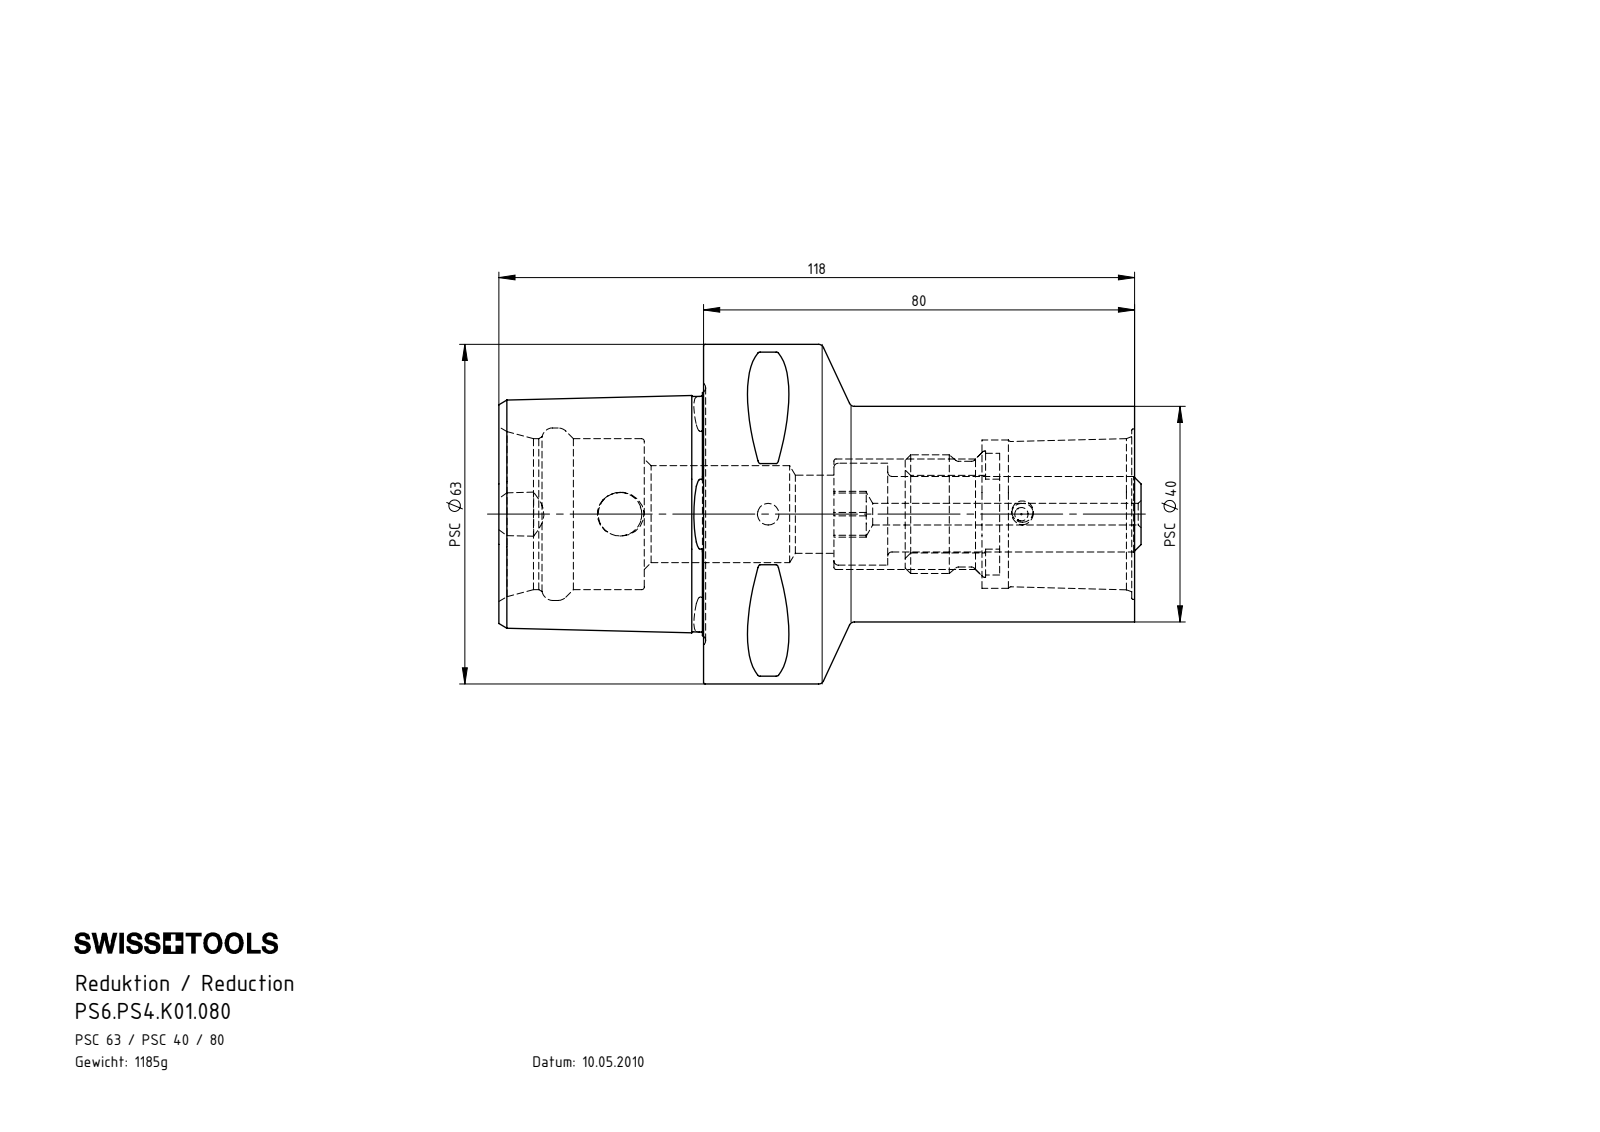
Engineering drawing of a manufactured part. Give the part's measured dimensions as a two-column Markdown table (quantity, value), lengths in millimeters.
| quantity | value |
| --- | --- |
| part name | ISO 8745-2.5x8_PreviewCfg; PS6-PS4.K01.080_B; PS6.PS4.K01.080; PS4-ER1.K01.047_A_PreviewCfg |
| STEP written by | SolidWorks 2017 (AUTOMOTIVE_DESIGN) |
| units | millimeters |
| bodies | 3 solids, 219 faces (44 planar, 52 cylindrical, 123 other) |
| overall size | 119.2 × 63 × 63 |
| volume | 155 298 mm³ |
| surface area | 34 927 mm² |
| round holes (diameter × count) | 4 × 3, 2.5 × 1, 8.1 × 1, 14.5 × 1, 18 × 1, 20.5 × 1, 28 × 1, 31.6 × 1, 32 × 1 |
| round bosses / shafts (diameter × count) | 63 × 1, 40 × 1, 18.9 × 1, 14 × 1 |
| partial cylindrical surfaces (radius × count) | 0.5 × 8, 7.95 × 3, 19.58 × 3, 6 × 1 |
| main face-to-face distances | 55.8, 38, 118, 80, 62.2, 24.2, 24.88, 27, 11, 35.2 |
| hole center spacings | 27.5, 47, 74.5 |
